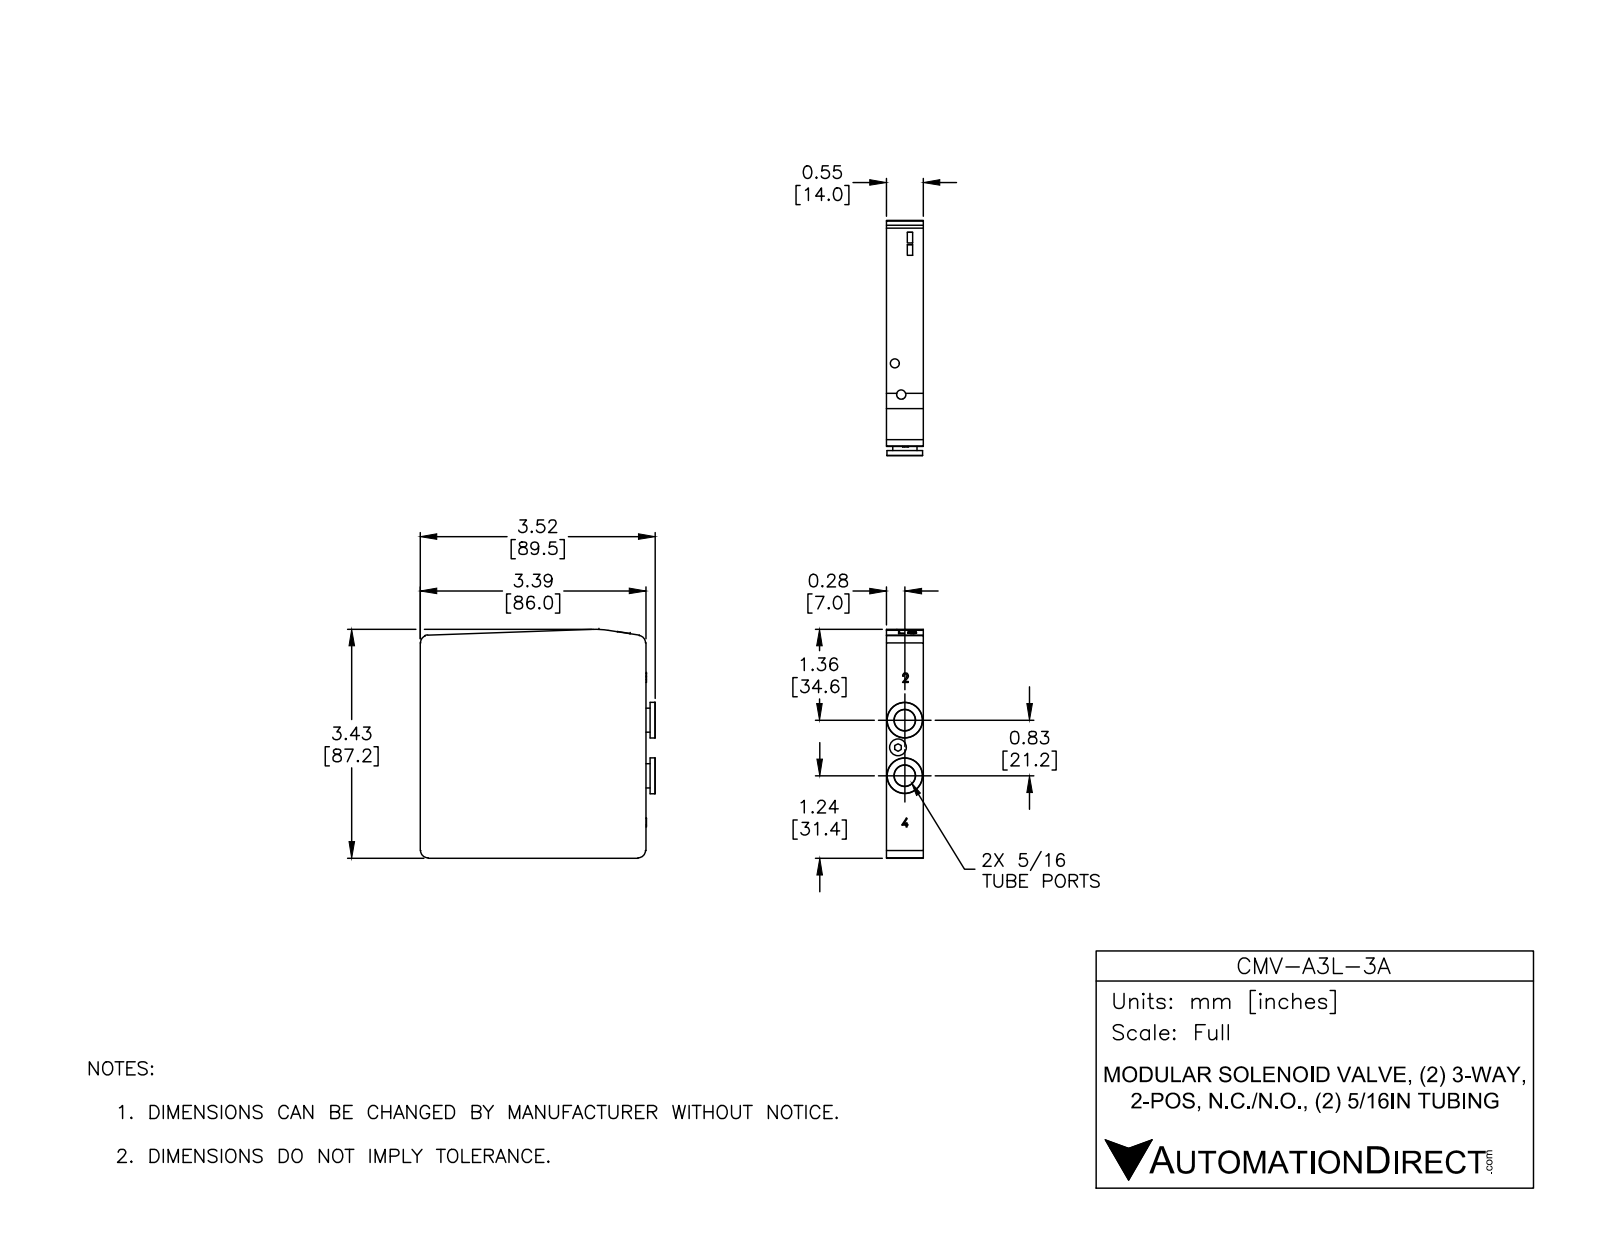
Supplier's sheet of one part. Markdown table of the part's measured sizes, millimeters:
| quantity | value |
| --- | --- |
| part name | CMV-A3L-3A |
| STEP written by | SolidWorks 2017 (AUTOMOTIVE_DESIGN) |
| units | millimeters |
| bodies | 1 solid, 157 faces (78 planar, 71 cylindrical, 8 other) |
| overall size | 89.5 × 87.22 × 14 |
| volume | 103 842 mm³ |
| surface area | 20 314 mm² |
| round holes (diameter × count) | 3.5 × 2, 8 × 2, 6.4 × 1 |
| round bosses / shafts (diameter × count) | 13.6 × 2, 9.2 × 2 |
| partial cylindrical surfaces (radius × count) | 2.8 × 4, 1.12 × 2, 1.37 × 2, 0.17 × 1, 0.55 × 1, 0.61 × 1, 0.61 × 1, 0.64 × 1 |
| main face-to-face distances | 14, 86, 89.5, 3.5, 1.6, 87.6, 1.9, 85.8, 2.5, 1.8 |
| hole center spacings | 10.72, 11.11, 12.14, 21.2 |
